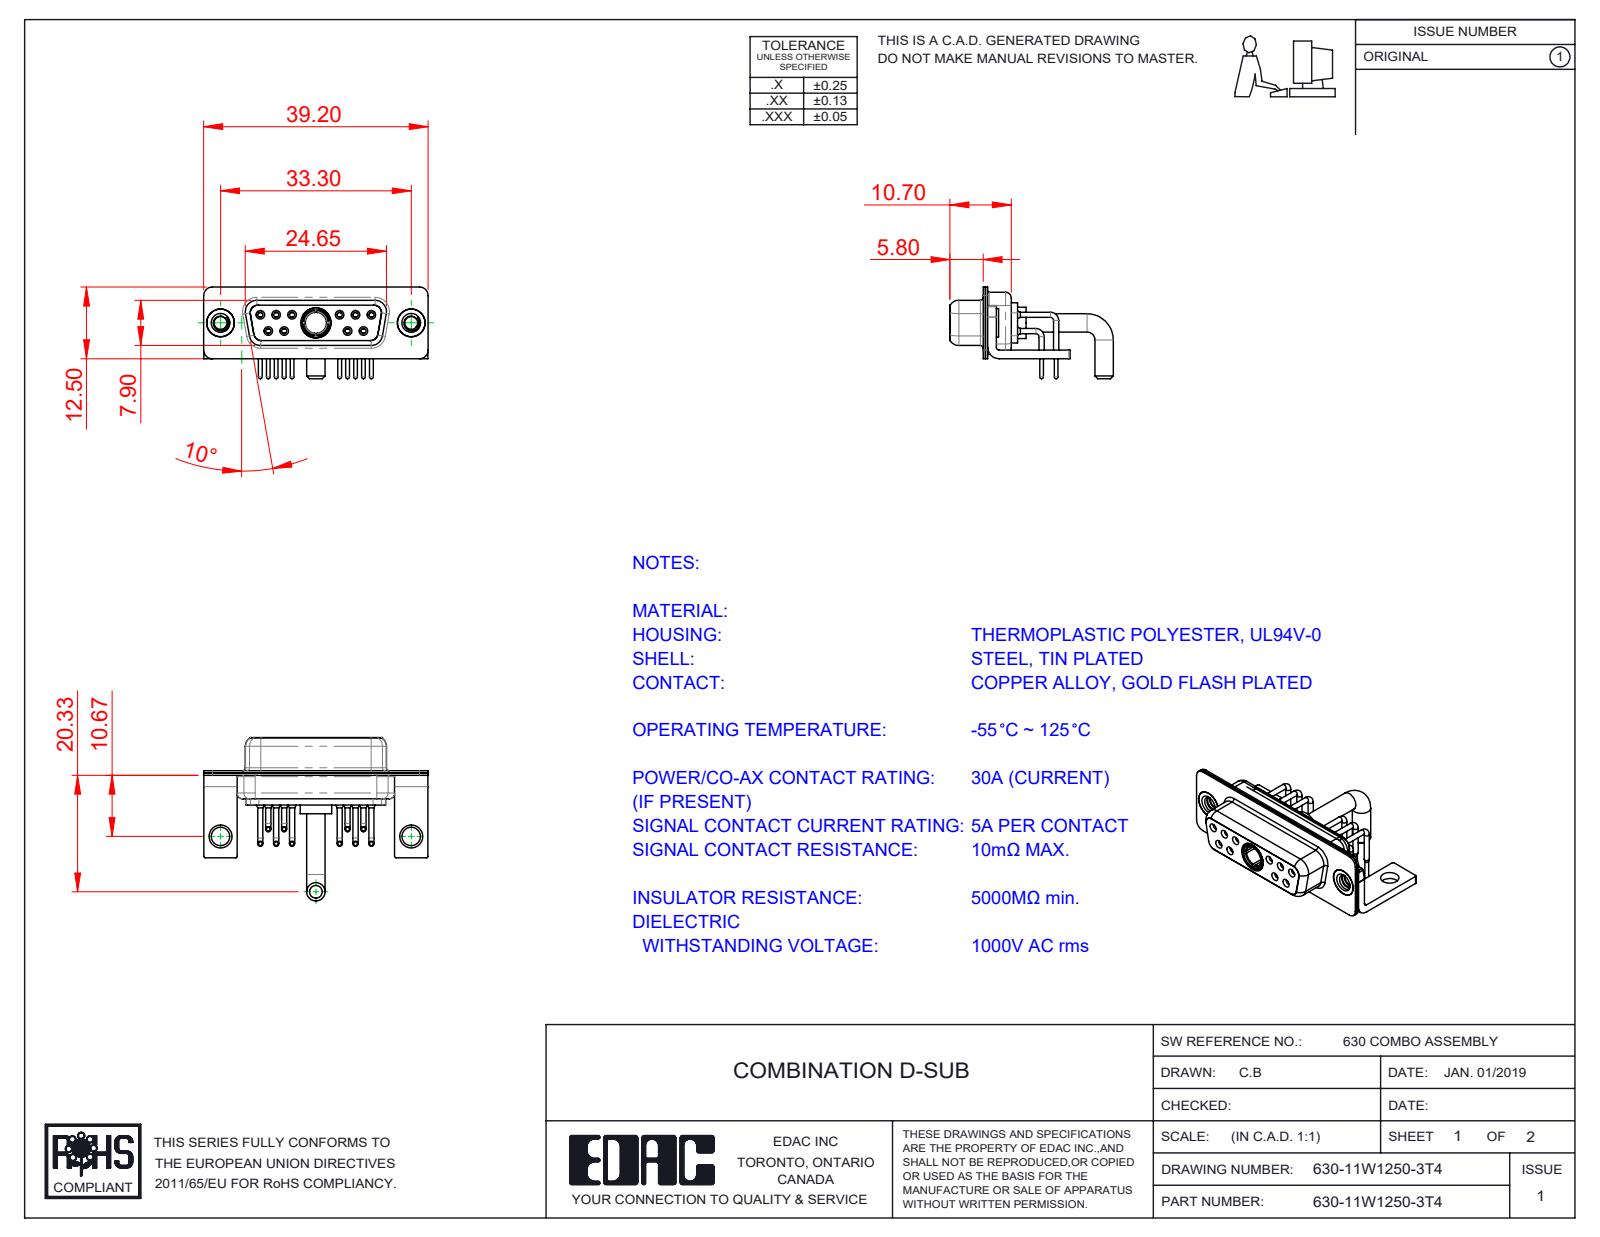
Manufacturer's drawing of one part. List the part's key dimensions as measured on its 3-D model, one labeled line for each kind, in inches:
Part name (STEP PRODUCT): 630Combo Contact Row 1; 630Combo Shell Front_15 Contacts; 630Combo Housing_11W1; 630Combo Stabilizer Bracket (+5 more)
STEP written by: SolidWorks 2020 (CONFIG_CONTROL_DESIGN)
Units: inches
Bodies: 19 solids, 927 faces (266 planar, 410 cylindrical, 251 other)
Overall size (bounding box): 1.543 × 1.123 × 0.63
Volume: 0.183 in³ · Surface area: 10.77 in²
Round holes (diameter × count): ⌀0.035 ×10, ⌀0.043 ×10, ⌀0.059 ×10, ⌀0.079 ×10, ⌀0.067 ×6, ⌀0.063 ×4, ⌀0.191 ×3, ⌀0.089 ×2, ⌀0.126 ×2, ⌀0.157 ×2, ⌀0.159 ×2, ⌀0.146 ×1
Round bosses / shafts (diameter × count): ⌀0.035 ×10, ⌀0.026 ×10, ⌀0.063 ×6, ⌀0.197 ×2, ⌀0.195 ×2, ⌀0.189 ×2, ⌀0.126 ×2, ⌀0.217 ×1
Partial cylindrical surfaces — rounded edges, fillets, slot ends (radius × count): R0.01 ×16, R0.059 ×16, R0.079 ×13, R0.053 ×12, R0.063 ×8, R0.02 ×5, R0.024 ×4, R0.026 ×4
Main face-to-face distances: 0.016, 0.031, 0.055, 0.018, 0.333, 0.059, 0.071, 0.35, 0.244, 0.091
Hole centre spacings: 0.124, 0.109, 0.545, 0.436, 0.654, 0.198, 0.198, 0.218
